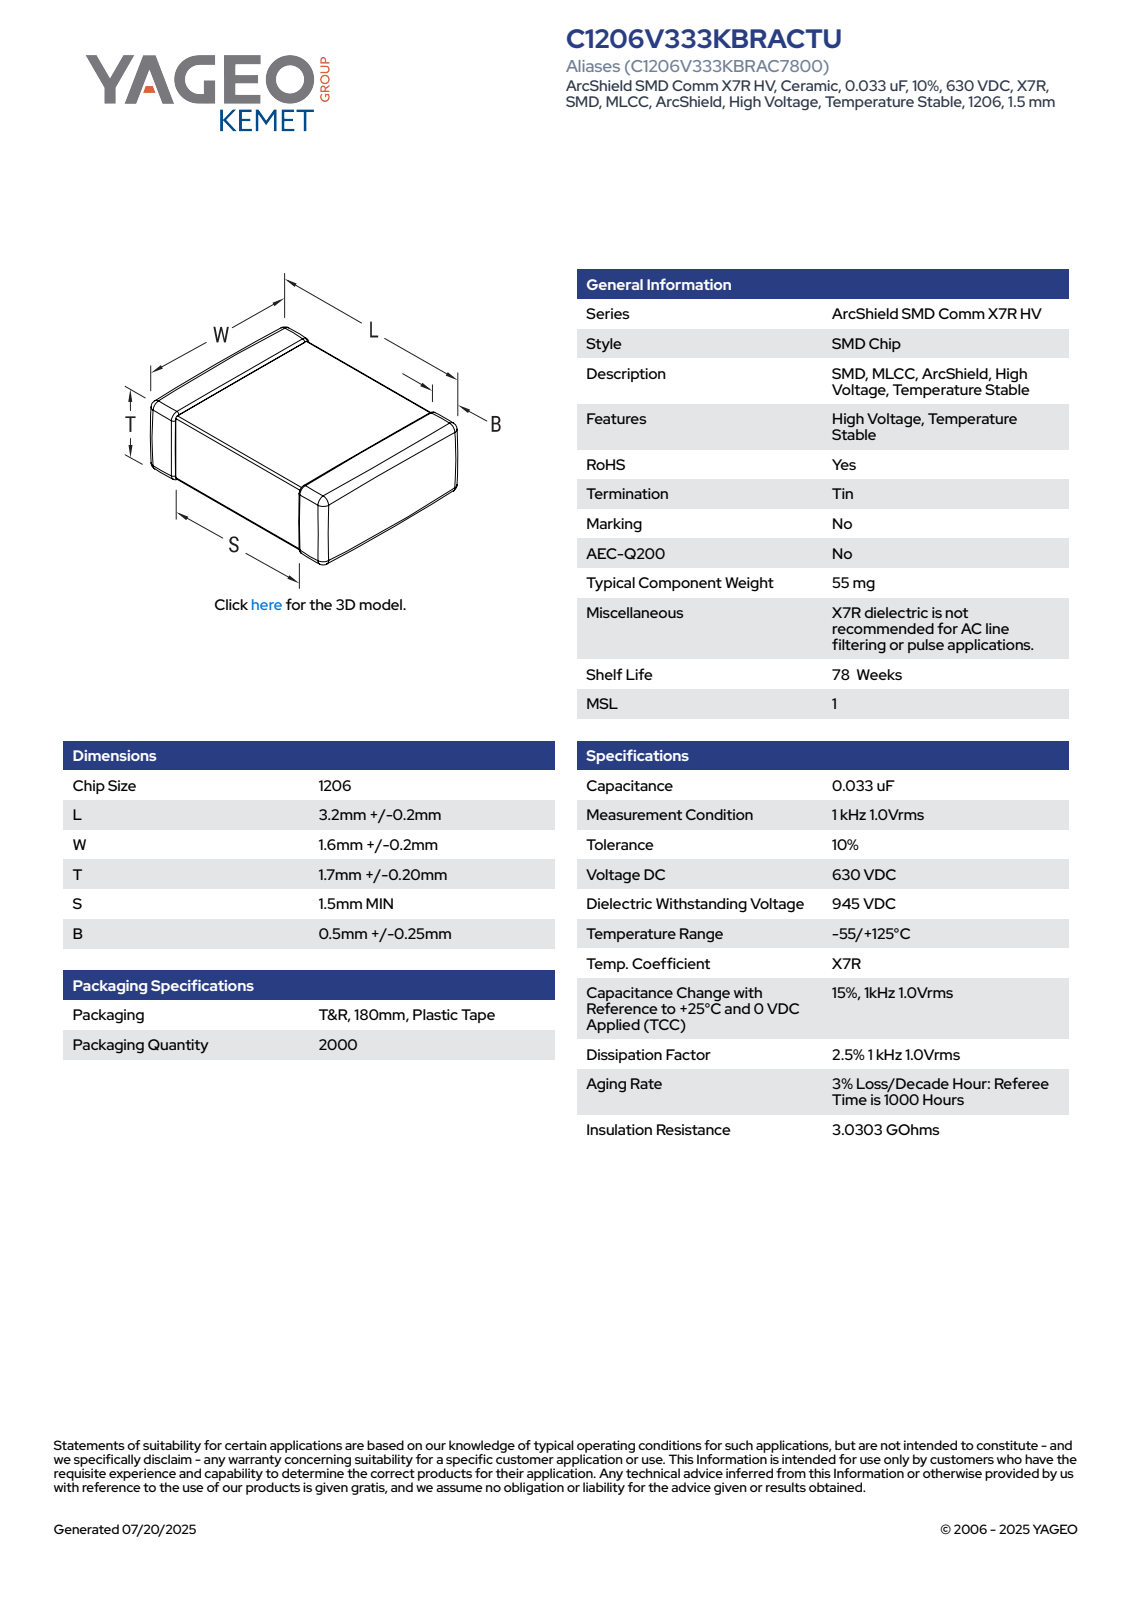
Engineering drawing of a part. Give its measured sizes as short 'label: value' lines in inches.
name: CCS_CCSTDNOS_1206_L3.4W1.8T1.9B0.75
written by: SolidWorks 2014 (AUTOMOTIVE_DESIGN)
unit: in
bodies: 4 solids, 125 faces (71 planar, 38 cylindrical, 16 other)
size: 0.134 × 0.075 × 0.071
volume: 0.001 in³; area: 0.05 in²
face distances: 0.069, 0.073, 0.068, 0.134, 0.072, 0.071, 0.075, 0.074, 0.072, 0.039
